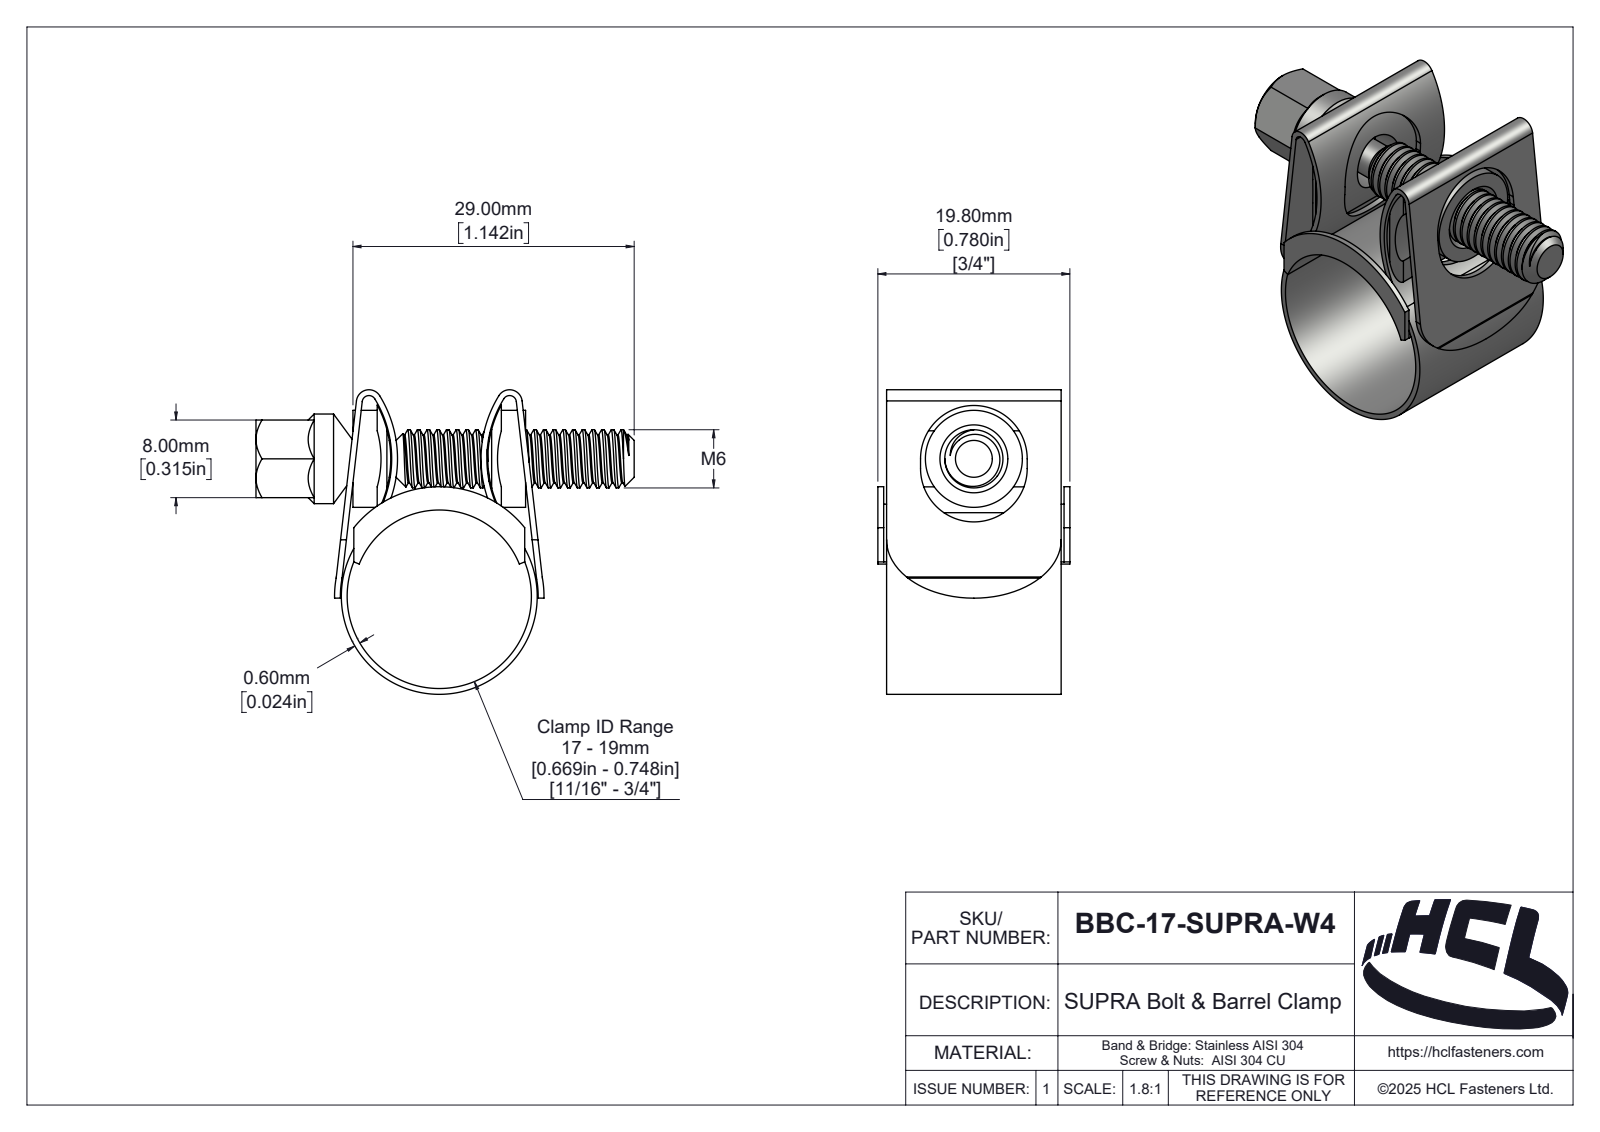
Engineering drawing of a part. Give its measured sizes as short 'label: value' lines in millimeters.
name: BBC-17-SUPRA-W4
written by: SolidWorks 2025 (AUTOMOTIVE_DESIGN)
unit: mm
bodies: 5 solids, 283 faces (44 planar, 159 cylindrical, 80 other)
size: 39 × 31.39 × 19.8
volume: 2 994 mm³; area: 6 800 mm²
holes: 1× ⌀19
bosses: 1× ⌀10, 1× ⌀9.24, 1× ⌀6, 1× ⌀3.8
rounds: 4× R1, 2× R0.7, 2× R1.3, 2× R2, 2× R2.6, 2× R5.5, 2× R10.73, 2× R11.73
face distances: 0.6, 0.9, 18.9, 2.5, 15.3, 19.2, 18.3, 8, 18, 12.8
